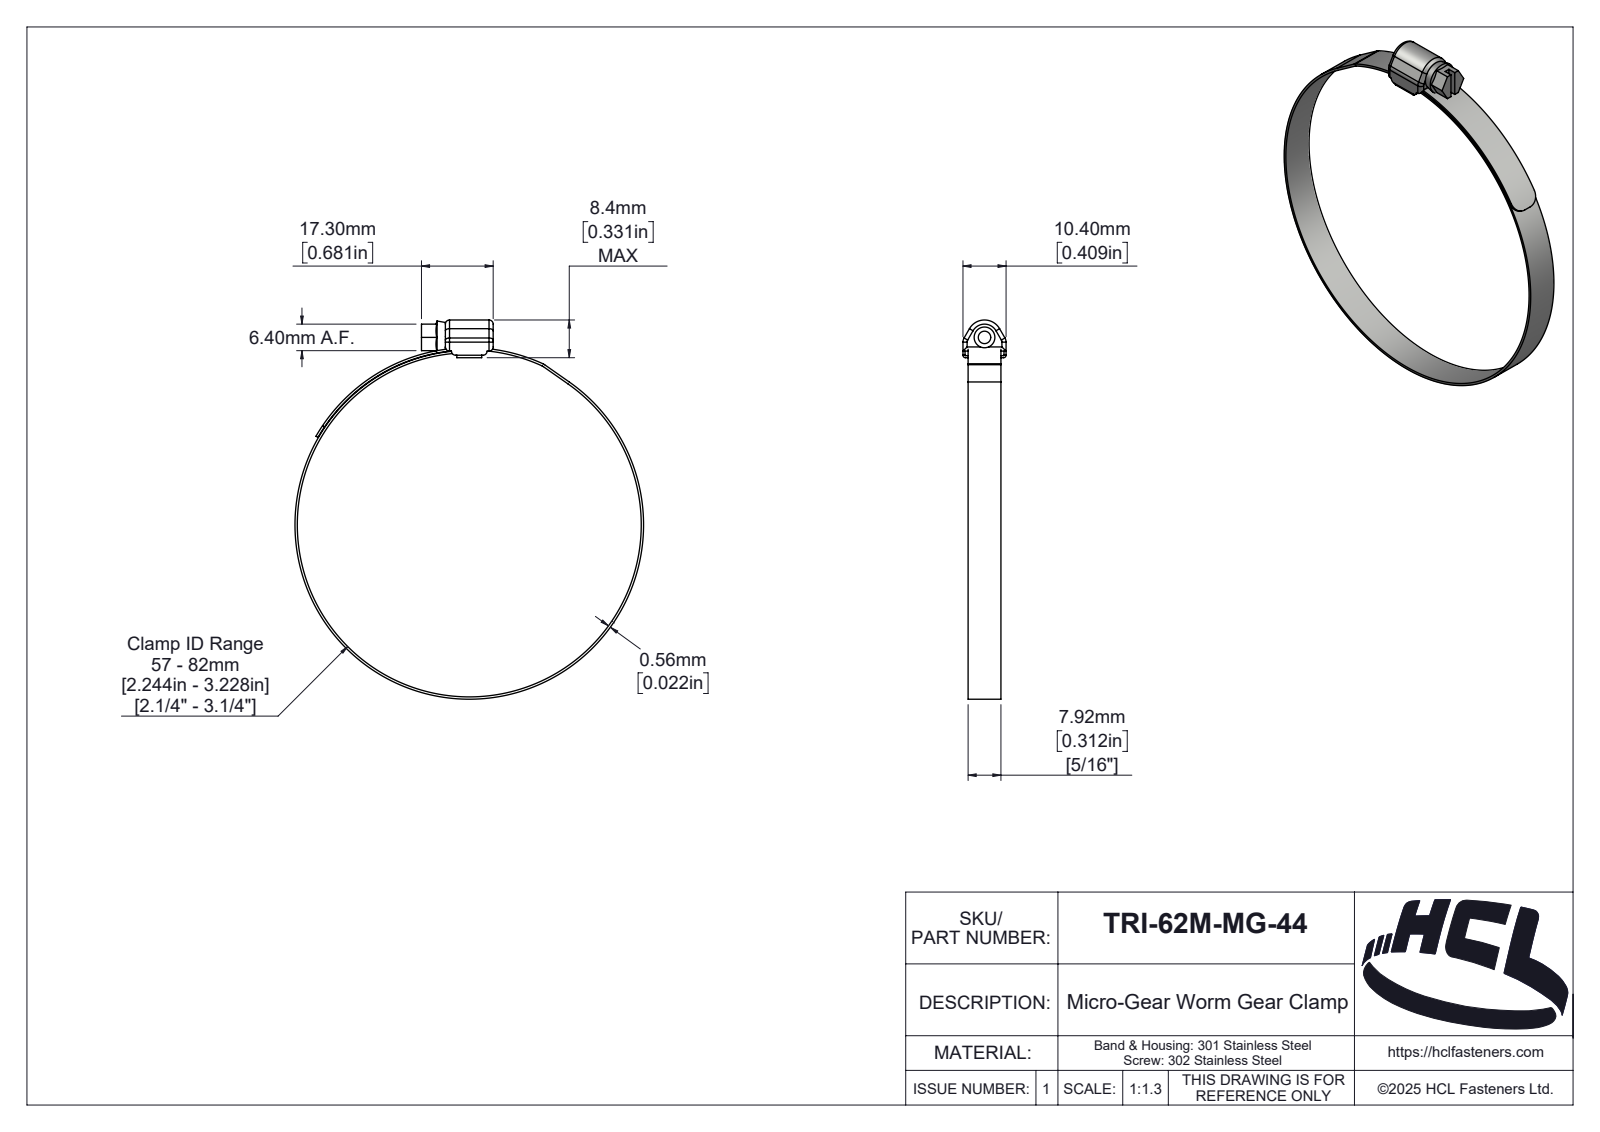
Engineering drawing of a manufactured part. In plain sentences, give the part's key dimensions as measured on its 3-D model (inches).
The part is named "TRI-62M-MG-44". Its 3-D file was written by "SolidWorks 2025 (AUTOMOTIVE_DESIGN)". It is 3 solids with 186 faces: 38 planar, 87 cylindrical and 61 other. Overall it measures 3.601 by 3.312 by 0.409 inches. Its volume is 0.141 cubic inches and its surface area 9.886 square inches. Round holes: 1 of diameter 0.197, 1 of diameter 3.268. Round bosses or shafts: 1 of diameter 3.312. Partial cylindrical surfaces (rounded edges, fillets, slot ends): 12 of radius 0.039, 3 of radius 0.079, 2 of radius 0.004, 2 of radius 0.024, 2 of radius 0.118, 1 of radius 0.01, 1 of radius 0.04, 1 of radius 0.05. The main face-to-face distances are 0.312, 0.043, 0.02, 0.049, 0.361, 0.022, 0.063, 0.244, 0.409, 0.227.
